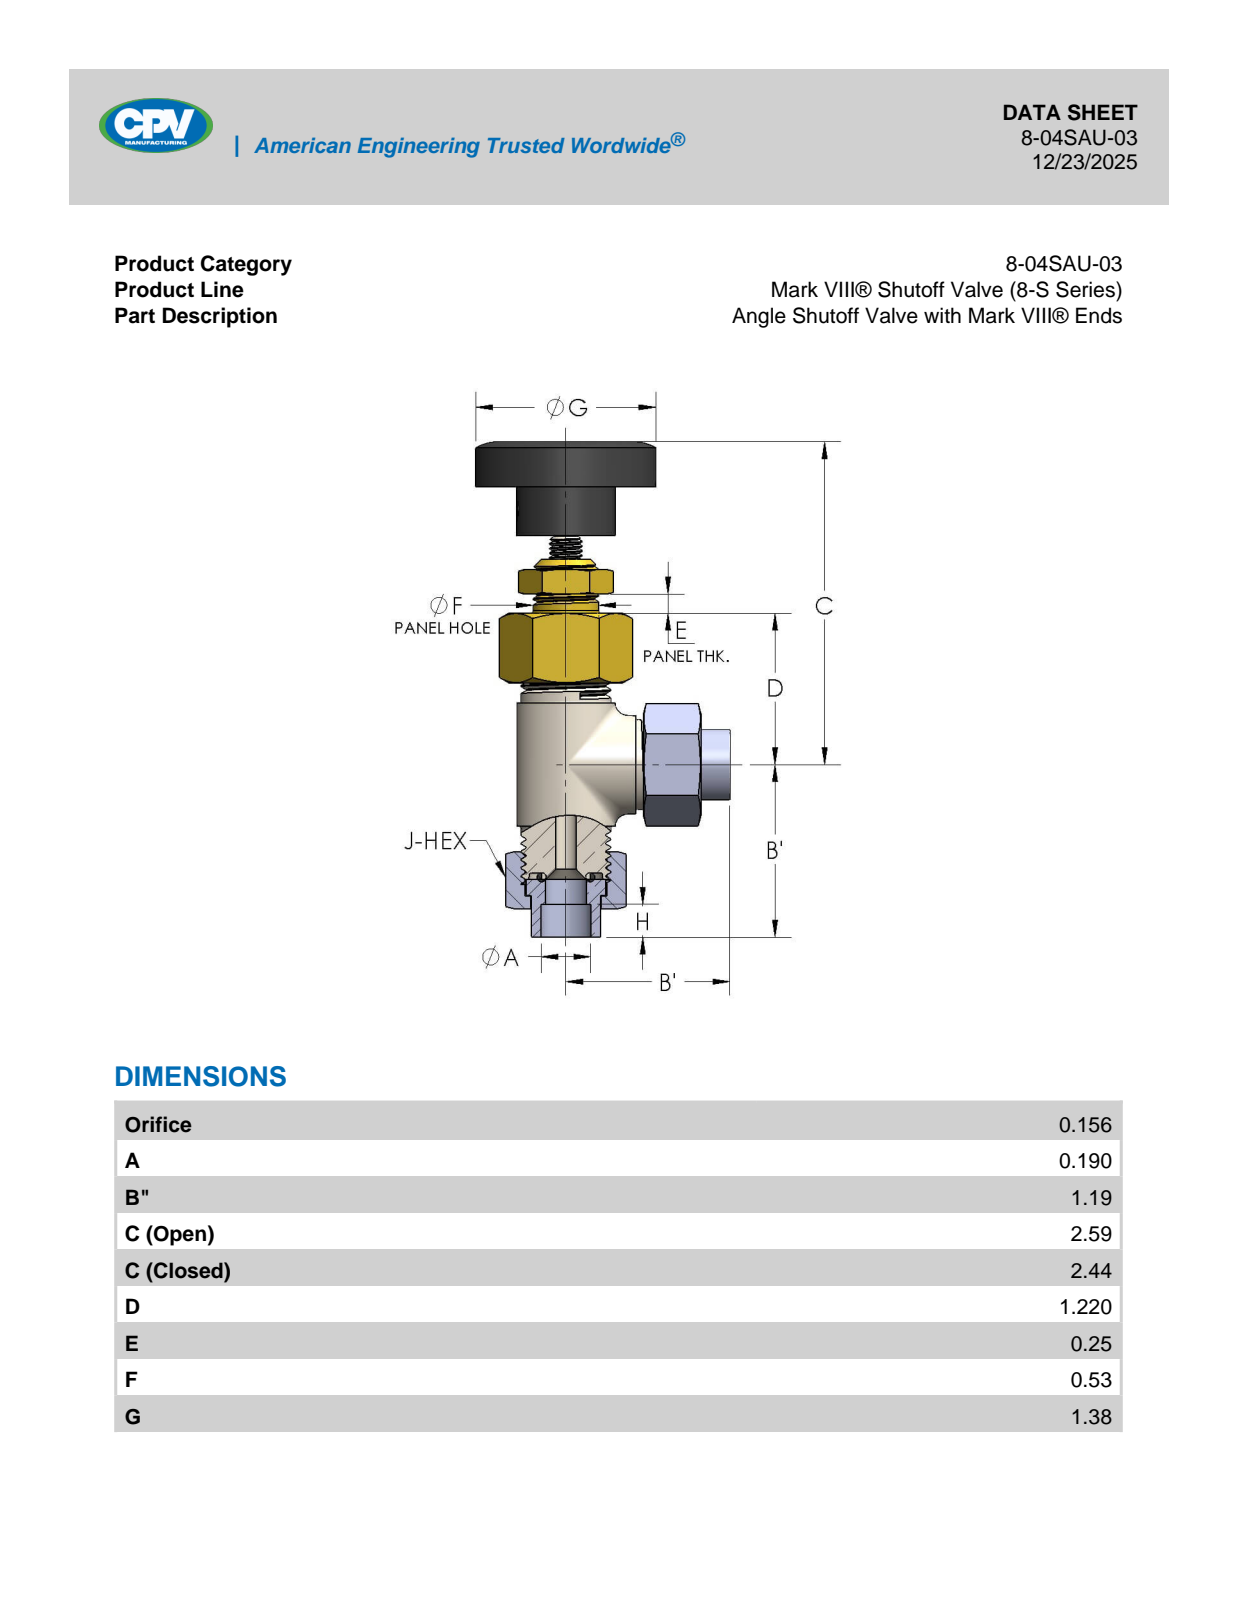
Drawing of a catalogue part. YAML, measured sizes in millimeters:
part_name: "8-04SAU-03"
step_written_by: "SolidWorks 2018 (AUTOMOTIVE_DESIGN)"
units: millimeters
bodies: {solids: 2, faces: 183, planar: 58, cylindrical: 44, other: 81}
overall_size: [93.7, 47.8, 35.1]
volume: 35590
surface_area: 11700
round_holes:
  - {diameter: 4, count: 2}
  - {diameter: 4.9, count: 2}
  - {diameter: 4.9, count: 1}
round_bosses_or_shafts:
  - {diameter: 14.2, count: 2}
  - {diameter: 8.7, count: 2}
  - {diameter: 35.1, count: 1}
  - {diameter: 19.1, count: 1}
  - {diameter: 17.3, count: 1}
  - {diameter: 12.6, count: 1}
  - {diameter: 6.4, count: 1}
  - {diameter: 4.8, count: 1}
face_to_face_distances: [19.1, 8.8, 3.2, 19.2, 22.4, 1.5, 17.5, 3.2, 20.7, 16]
